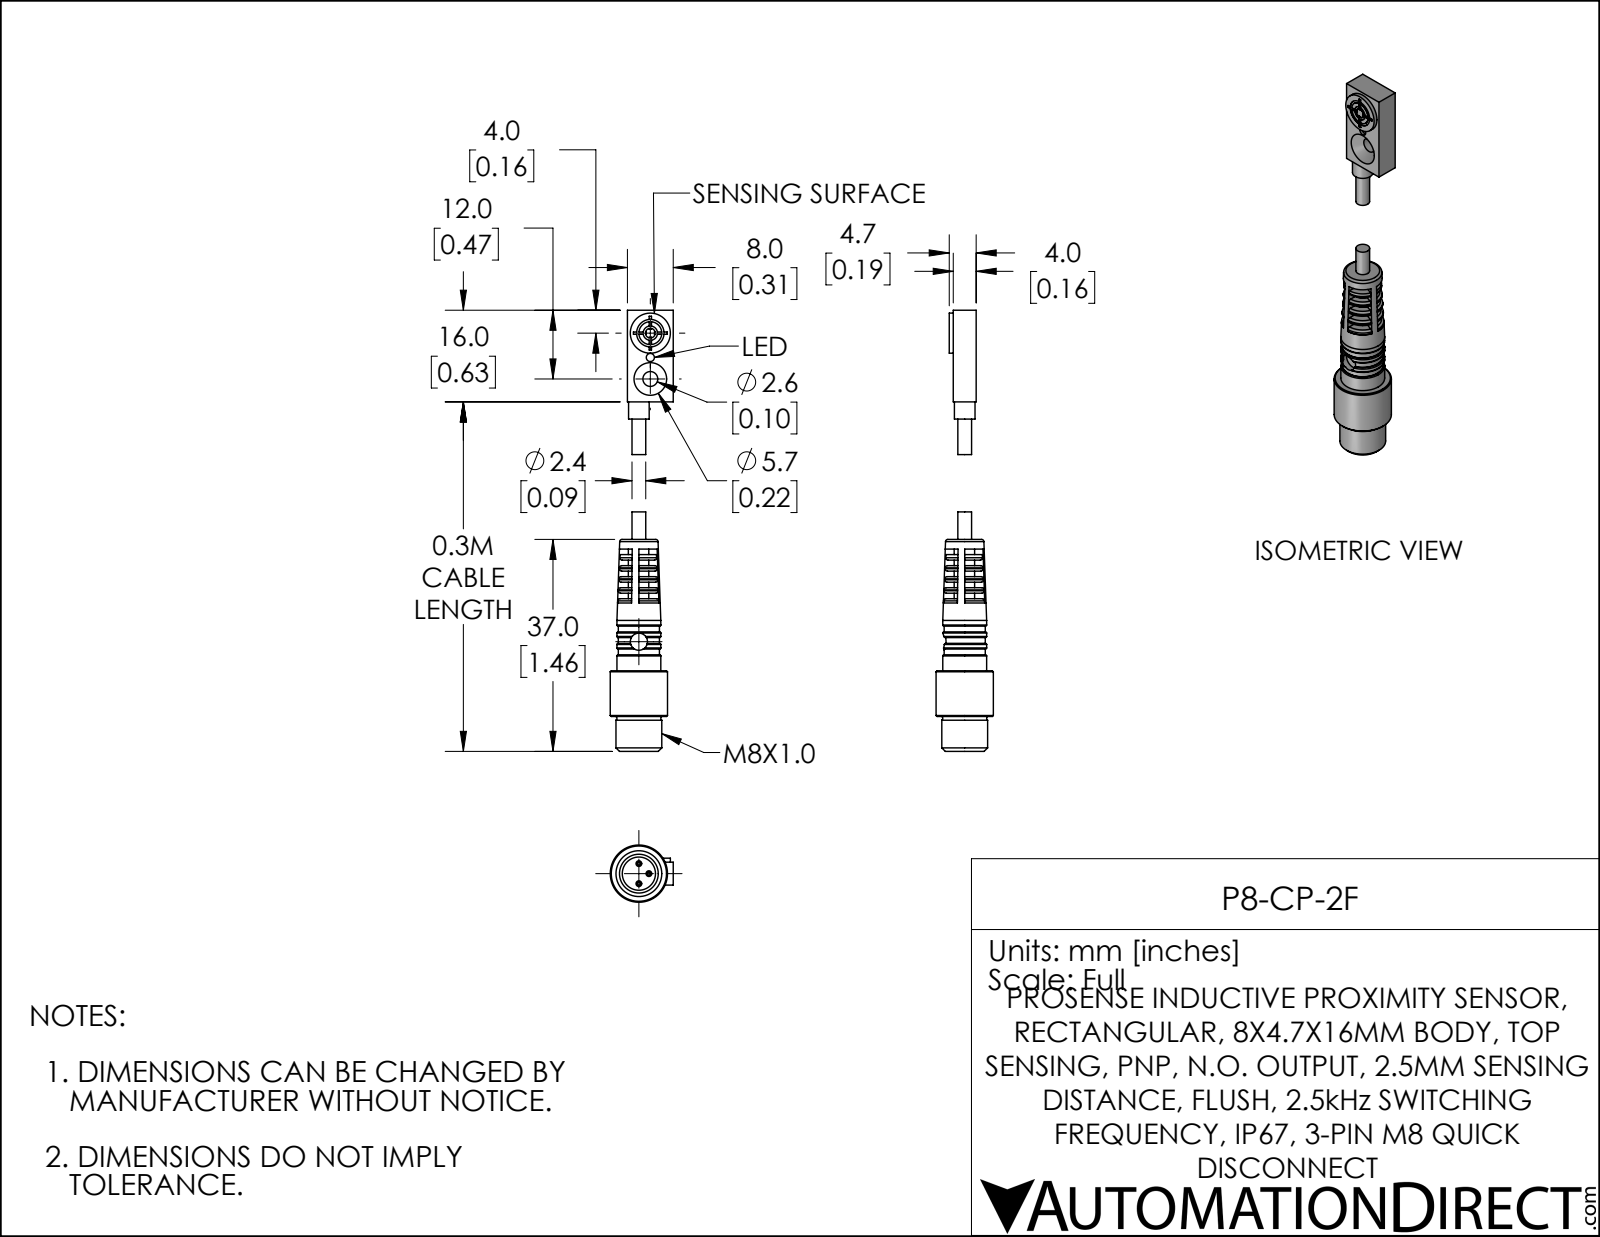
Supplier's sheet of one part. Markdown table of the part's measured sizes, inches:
| quantity | value |
| --- | --- |
| part name | P8-CP-2F_1; P8-CP-2F_2; P8-CP-2F |
| STEP written by | SolidWorks 2019 (AUTOMOTIVE_DESIGN) |
| units | inches |
| bodies | 2 solids, 240 faces (116 planar, 56 cylindrical, 68 other) |
| overall size | 2.918 × 0.433 × 0.394 |
| volume | 0.135 in³ |
| surface area | 3.16 in² |
| round holes (diameter × count) | 0.056 × 1, 0.098 × 1, 0.102 × 1, 0.118 × 1, 0.189 × 1, 0.228 × 1 |
| round bosses / shafts (diameter × count) | 0.039 × 3, 0.394 × 1, 0.315 × 1, 0.302 × 1, 0.283 × 1, 0.276 × 1, 0.157 × 1, 0.142 × 1 |
| partial cylindrical surfaces (radius × count) | 0.033 × 1, 0.072 × 1 |
| main face-to-face distances | 0.038, 0.152, 0.114, 0.315, 0.157, 0.076, 0.076, 0.189, 0.303, 0.265 |
| hole center spacings | 0.148, 0.167, 0.315 |
